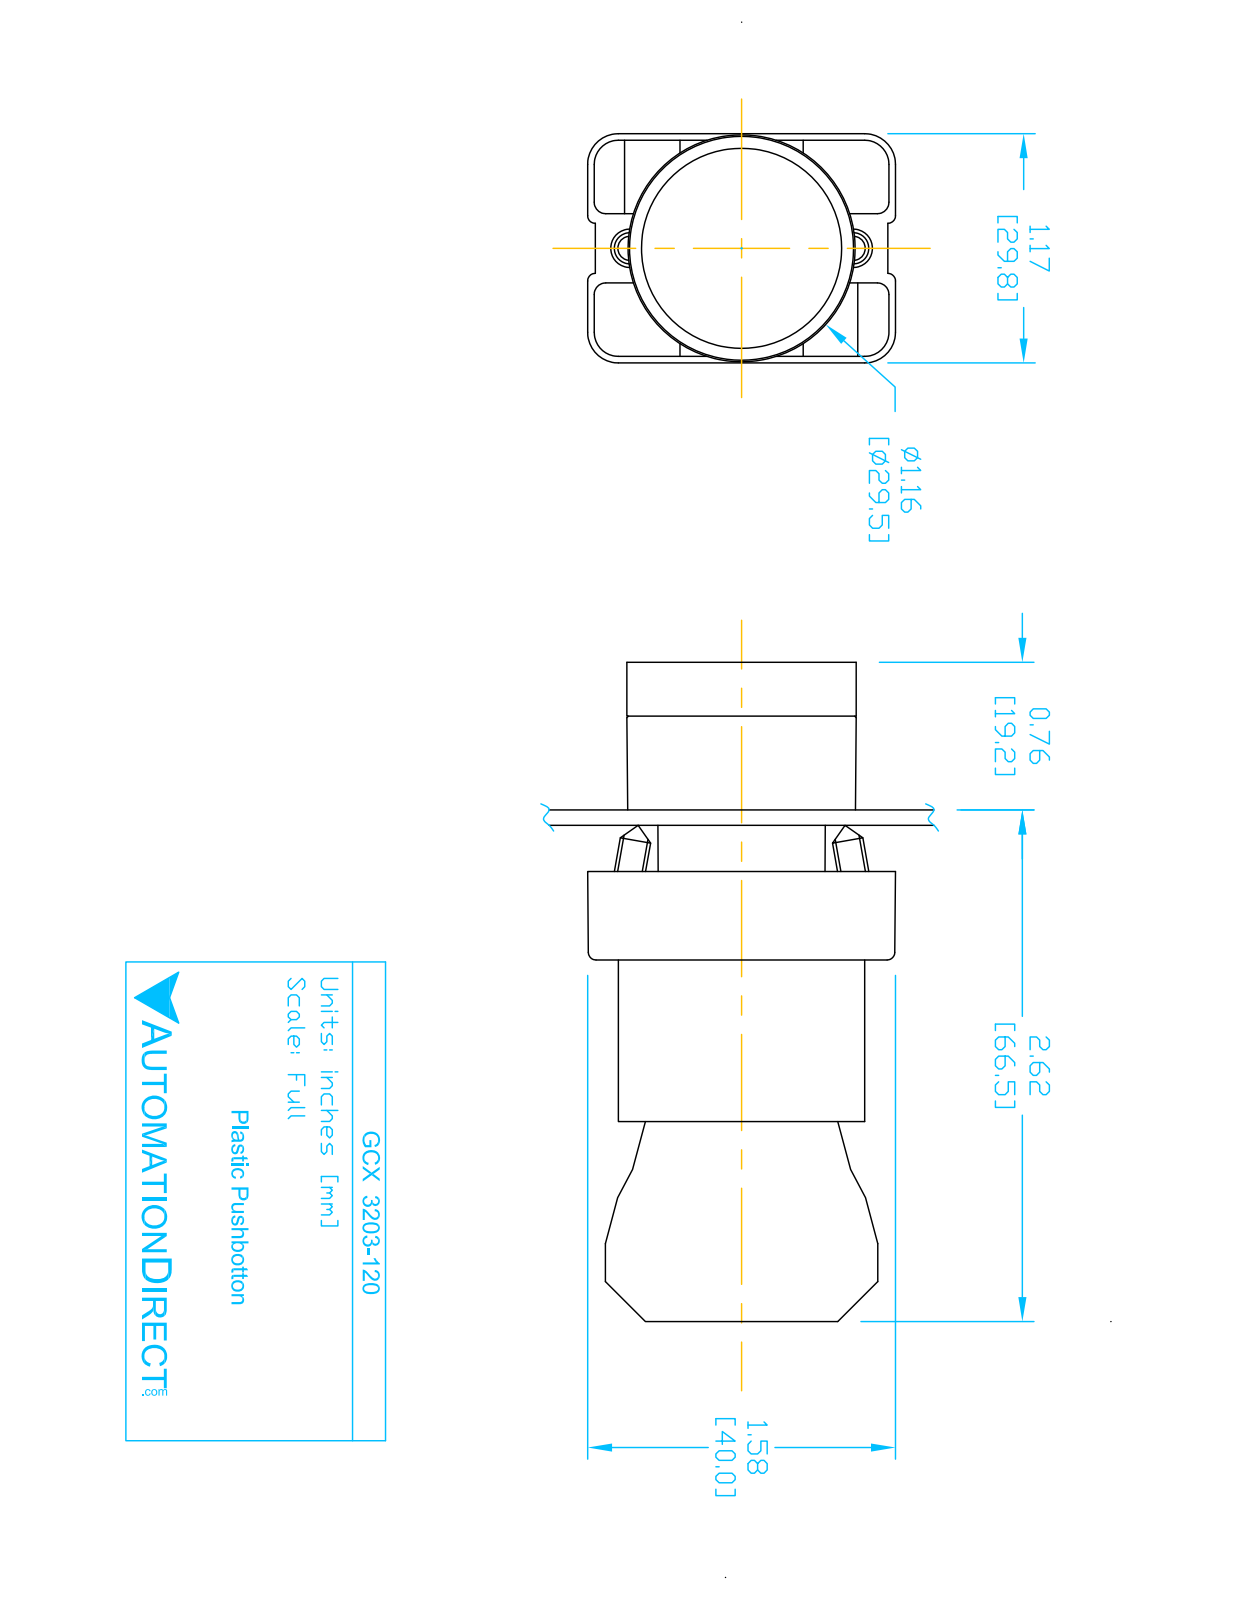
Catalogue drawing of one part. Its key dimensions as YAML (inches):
part_name: "GCX3203-120; ECX3029-2; GCX3203 OPERATOR; ECX1050 (+1 more)"
step_written_by: "SolidWorks 2016 (AUTOMOTIVE_DESIGN)"
units: inches
bodies: {solids: 8, faces: 431, planar: 252, cylindrical: 148, other: 31}
overall_size: [3.319, 1.581, 1.177]
volume: 2.794
surface_area: 38.77
round_holes:
  - {diameter: 0.079, count: 2}
  - {diameter: 0.124, count: 2}
  - {diameter: 0.13, count: 2}
  - {diameter: 0.087, count: 1}
  - {diameter: 0.197, count: 1}
  - {diameter: 0.469, count: 1}
  - {diameter: 0.878, count: 1}
  - {diameter: 0.888, count: 1}
  - {diameter: 1.024, count: 1}
round_bosses_or_shafts:
  - {diameter: 0.157, count: 4}
  - {diameter: 1.175, count: 1}
  - {diameter: 1.004, count: 1}
  - {diameter: 0.945, count: 1}
  - {diameter: 0.856, count: 1}
  - {diameter: 0.78, count: 1}
  - {diameter: 0.504, count: 1}
partial_cylinders:
  - {radius: 0.059, count: 24}
  - {radius: 0.041, count: 12}
  - {radius: 0.124, count: 12}
  - {radius: 0.157, count: 12}
  - {radius: 0.039, count: 8}
  - {radius: 0.128, count: 2}
  - {radius: 0.02, count: 1}
  - {radius: 0.063, count: 1}
face_to_face_distances: [0.827, 0.579, 2.02, 1.193, 1.171, 0.276, 2.295, 1.469, 0.031, 0.033]
hole_center_spacings: [0.236, 0.544, 0.472, 0.49]
